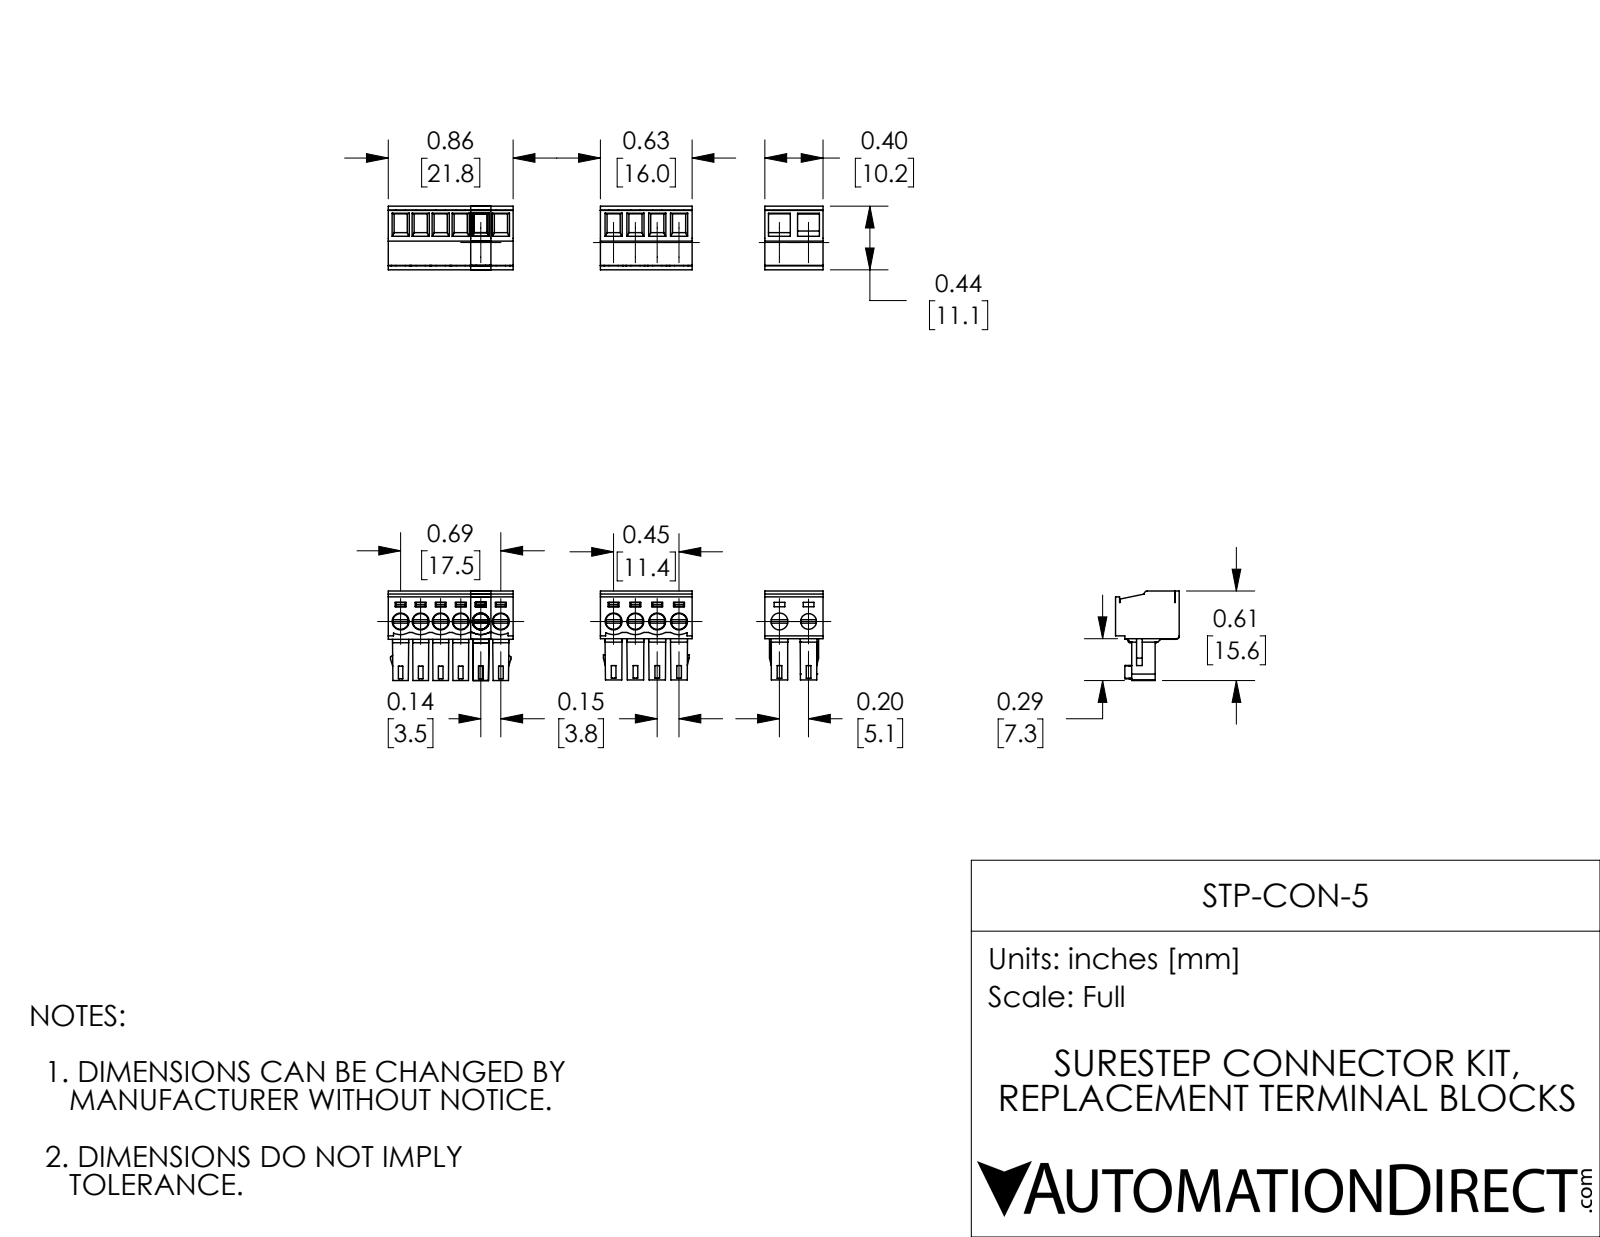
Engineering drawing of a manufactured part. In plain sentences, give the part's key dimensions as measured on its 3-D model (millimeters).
The part is named "STP-CON-5". Its 3-D file was written by "SolidWorks 2017 (AUTOMOTIVE_DESIGN)". It is 4 solids with 1399 faces: 1049 planar, 259 cylindrical and 91 other. Overall it measures 75.9 by 15.6 by 11.1 millimeters. Its volume is 5 080 cubic millimeters and its surface area 5 632 square millimeters. Round holes: 12 of diameter 2, 11 of diameter 2.9, 2 of diameter 1.2, 1 of diameter 2.7. Round bosses or shafts: 10 of diameter 2.9. Partial cylindrical surfaces (rounded edges, fillets, slot ends): 73 of radius 0.2, 28 of radius 0.3, 12 of radius 1.9, 10 of radius 2.9, 5 of radius 0.5, 2 of radius 1.3, 1 of radius 0.6. The main face-to-face distances are 3.5, 8.3, 2.8, 11.1, 7, 10.5, 0.7, 6.3, 3.8, 0.8. The hole center spacings are 3.5, 7, 3.8, 10.5, 7.6, 14, 5.1, 11.4.
